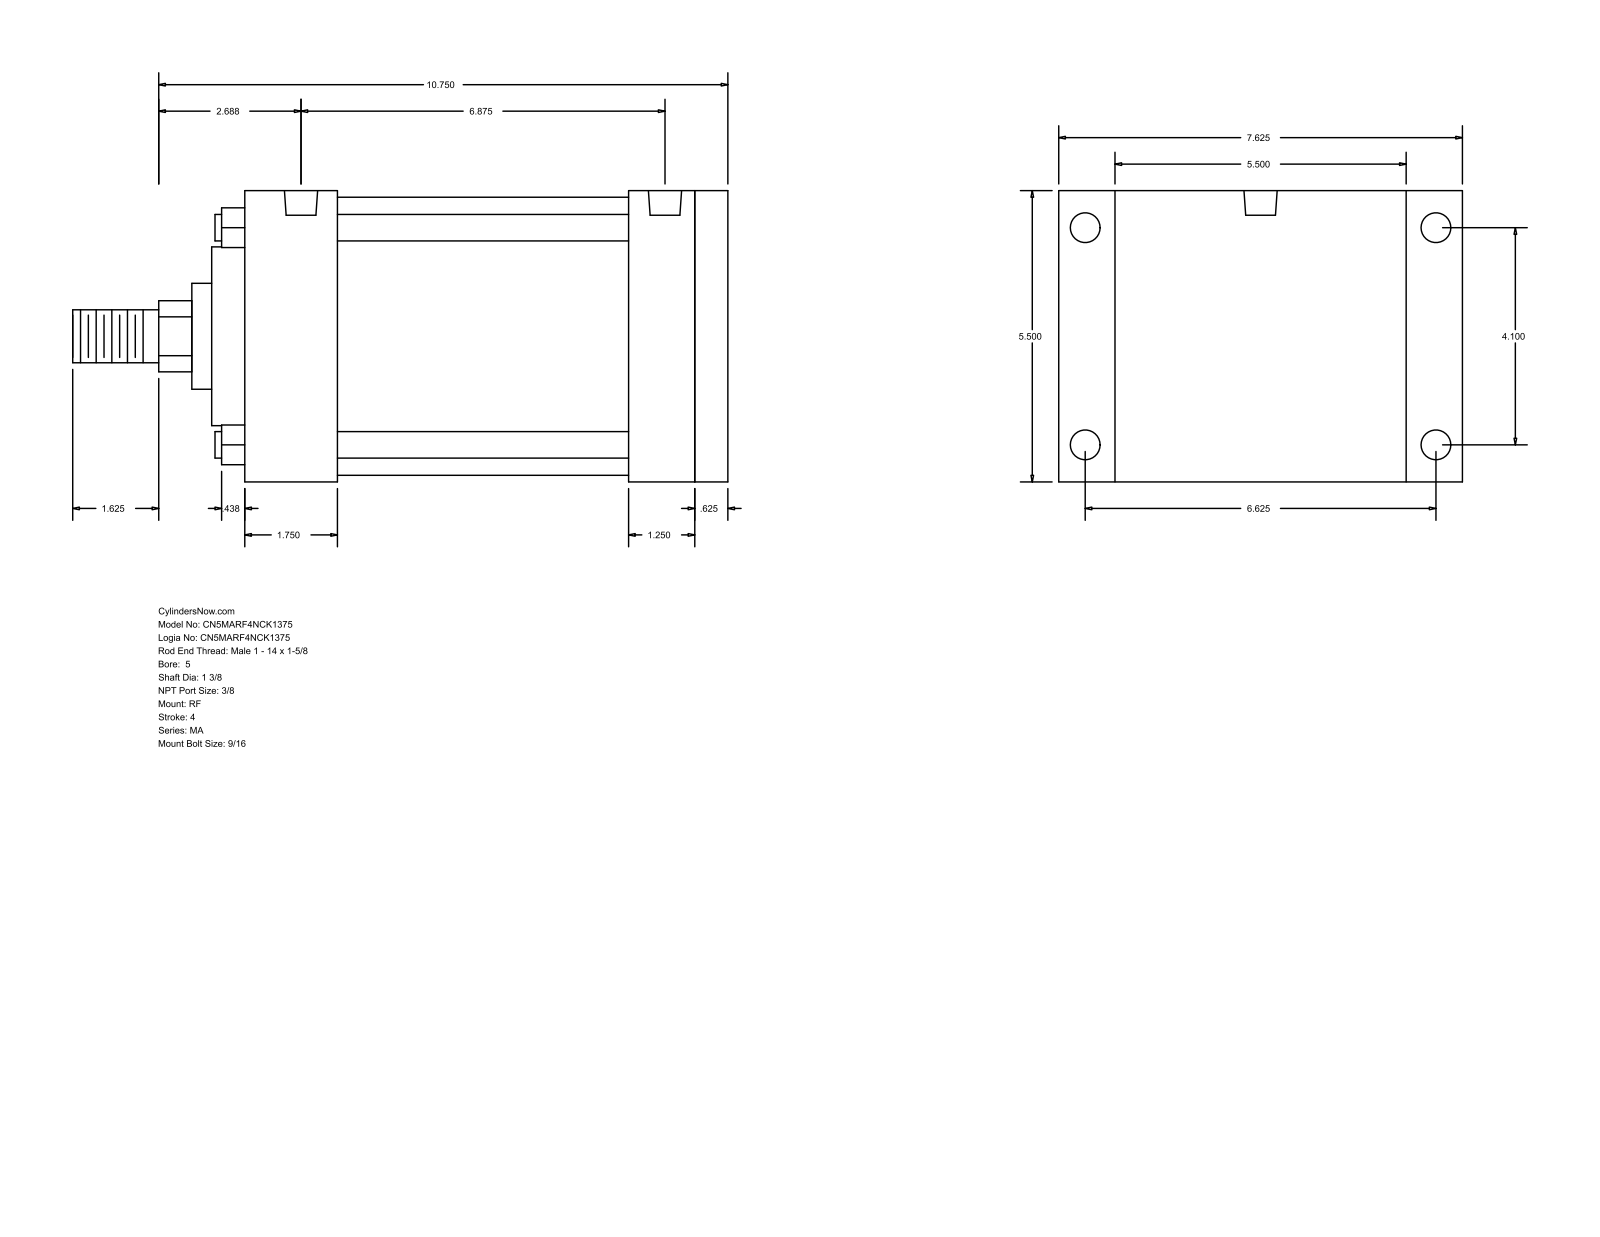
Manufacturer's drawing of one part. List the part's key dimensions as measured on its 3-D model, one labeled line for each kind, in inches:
Part name (STEP PRODUCT): MA_RF__0500_1.375
STEP written by: GSSL Pune (CONFIG_CONTROL_DESIGN)
Units: inches
Bodies: 0 solids, 94 faces (65 planar, 29 cylindrical, 0 other)
Overall size (bounding box): 12.375 × 7.625 × 5.5
Round holes (diameter × count): ⌀0.437 ×4, ⌀0.563 ×4, ⌀0.627 ×2
Round bosses / shafts (diameter × count): ⌀0.5 ×4, ⌀5.25 ×1, ⌀3.375 ×1, ⌀2 ×1, ⌀1.375 ×1, ⌀1 ×1
Partial cylindrical surfaces — rounded edges, fillets, slot ends (radius × count): R0.672 ×1
Main face-to-face distances: 5.5, 9.125, 0.625, 8.5, 1.75, 6.75, 7.375, 7.25, 5.5, 1.25
Hole centre spacings: 0.188, 4.1, 6.5, 6.625, 6.687, 7.791, 6.875
